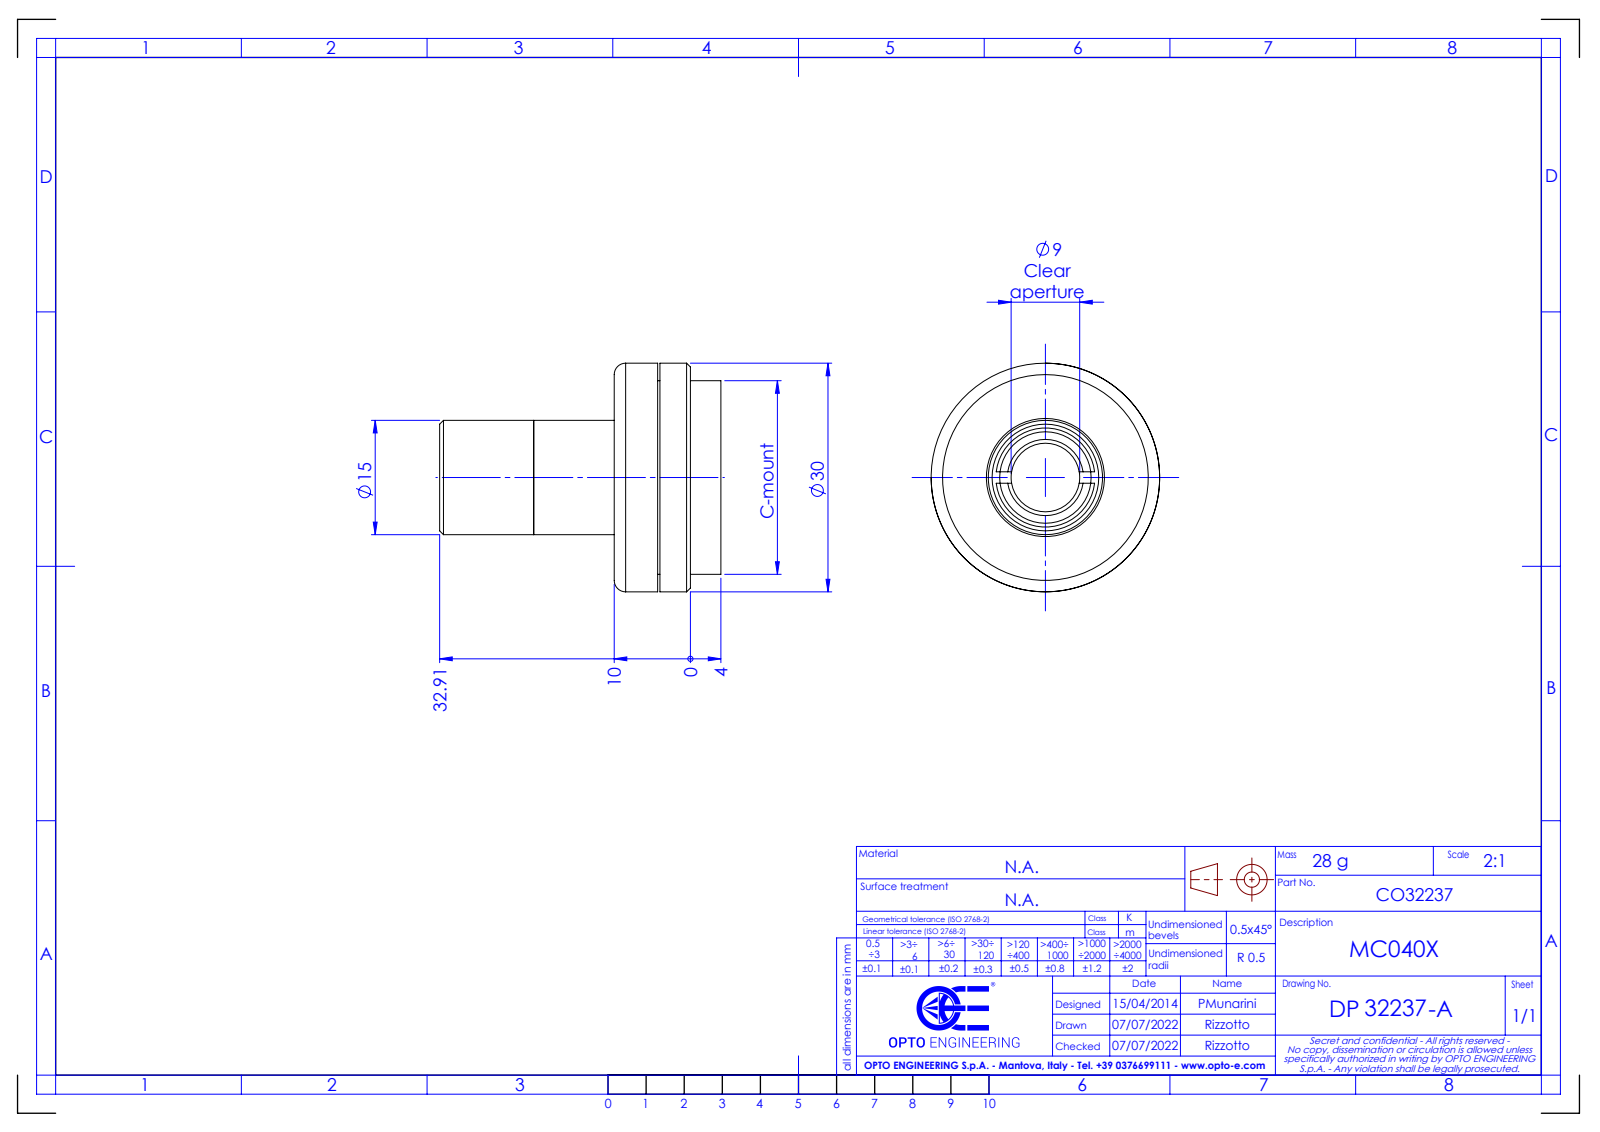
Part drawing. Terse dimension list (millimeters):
name: DP32237-A_MC040X
written by: SolidWorks 2021 (CONFIG_CONTROL_DESIGN)
unit: mm
bodies: 0 solids, 48 faces (15 planar, 18 cylindrical, 15 other)
size: 36.91 × 30 × 30
holes: 1× ⌀9, 1× ⌀12
bosses: 1× ⌀30, 1× ⌀25.4, 1× ⌀15, 1× ⌀14.5
face distances: 4, 6, 5.7, 10, 4.3, 14, 8.3, 8, 22.91, 28.61
